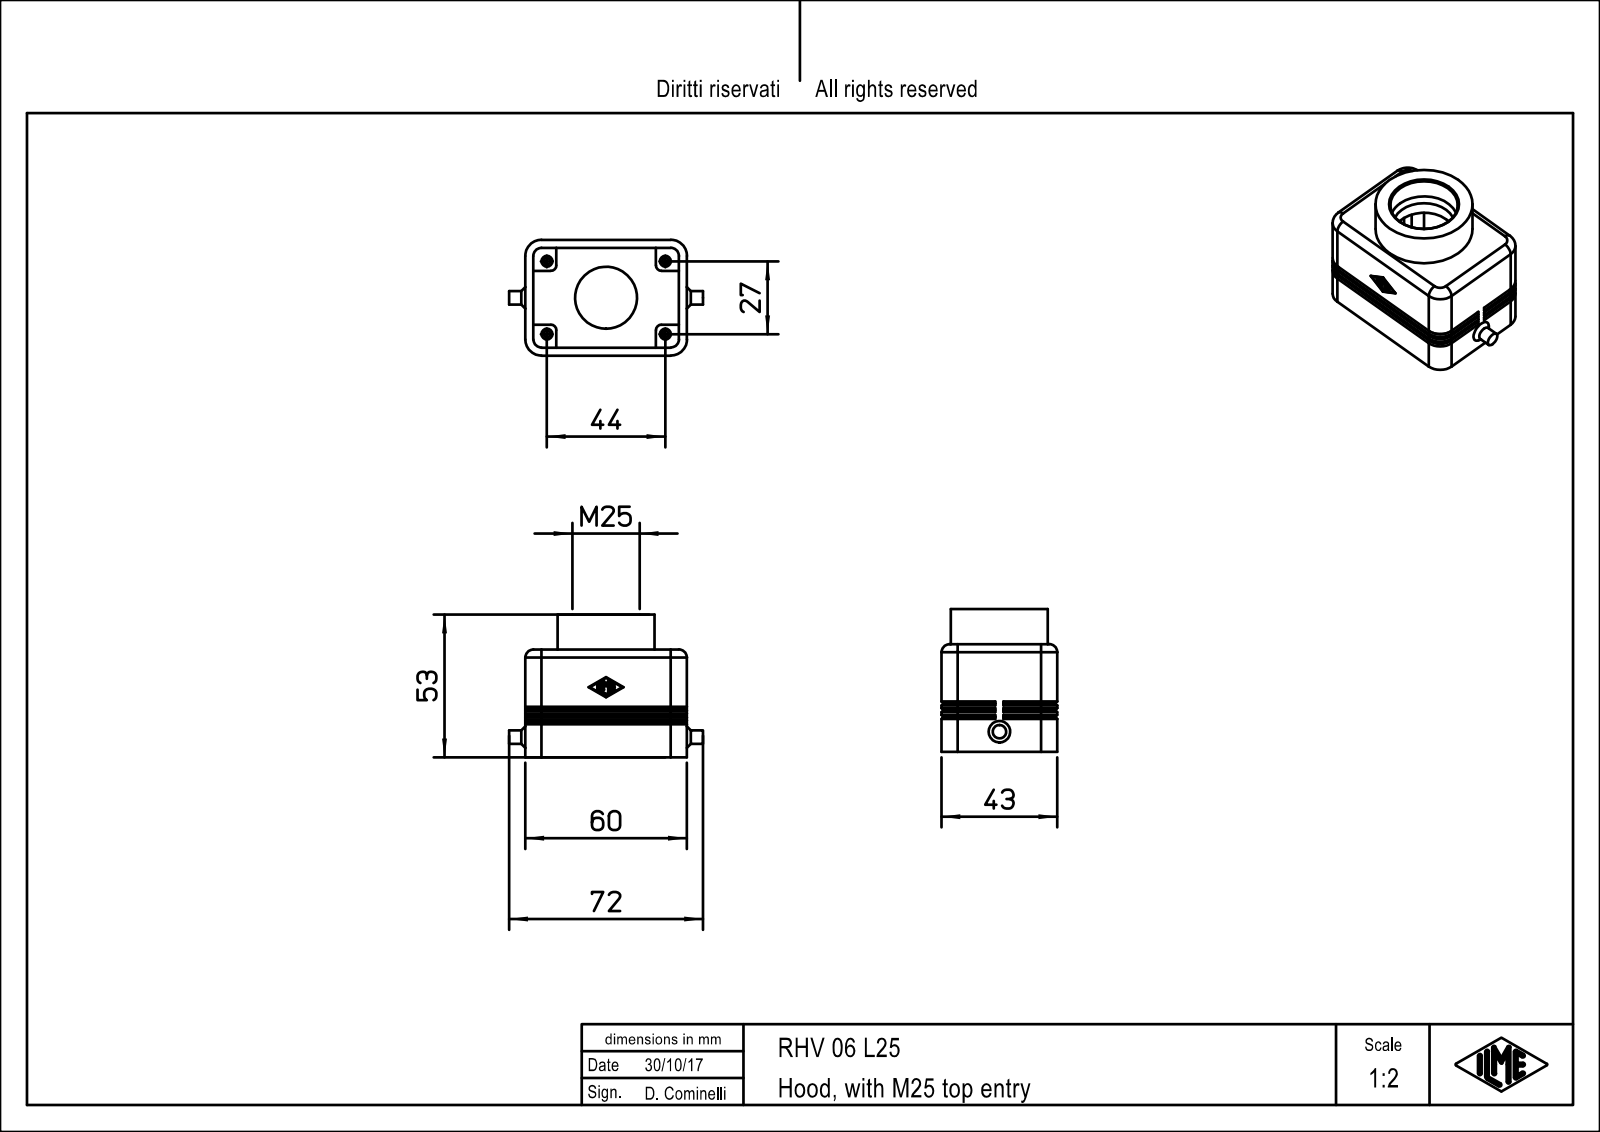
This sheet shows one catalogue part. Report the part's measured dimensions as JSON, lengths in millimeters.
{"part_name": "RHV_06_L25", "step_written_by": "PTC Creo Elements/Direct Modeling 19.0E 27-Jun-2016 (C) Parametric Technology GmbH (AUTOMOTIVE_DESIGN)", "units": "millimeters", "bodies": {"solids": 1, "faces": 263, "planar": 139, "cylindrical": 80, "other": 44}, "overall_size": [72, 53, 43], "volume_mm3": 41165, "surface_area_mm2": 21909, "round_holes": [[2.46, 4], [4, 4], [23, 1], [25, 1]], "round_bosses_or_shafts": [[36, 1], [5, 1]], "partial_cylinders_radius": [[0.25, 14], [3, 8], [2, 4], [5.3, 4], [6, 4]], "face_to_face_distances": [3, 40, 37, 57, 43, 11.5, 8.5, 60, 54, 48.5], "hole_center_spacings": [25.81, 27, 44, 51.62]}
